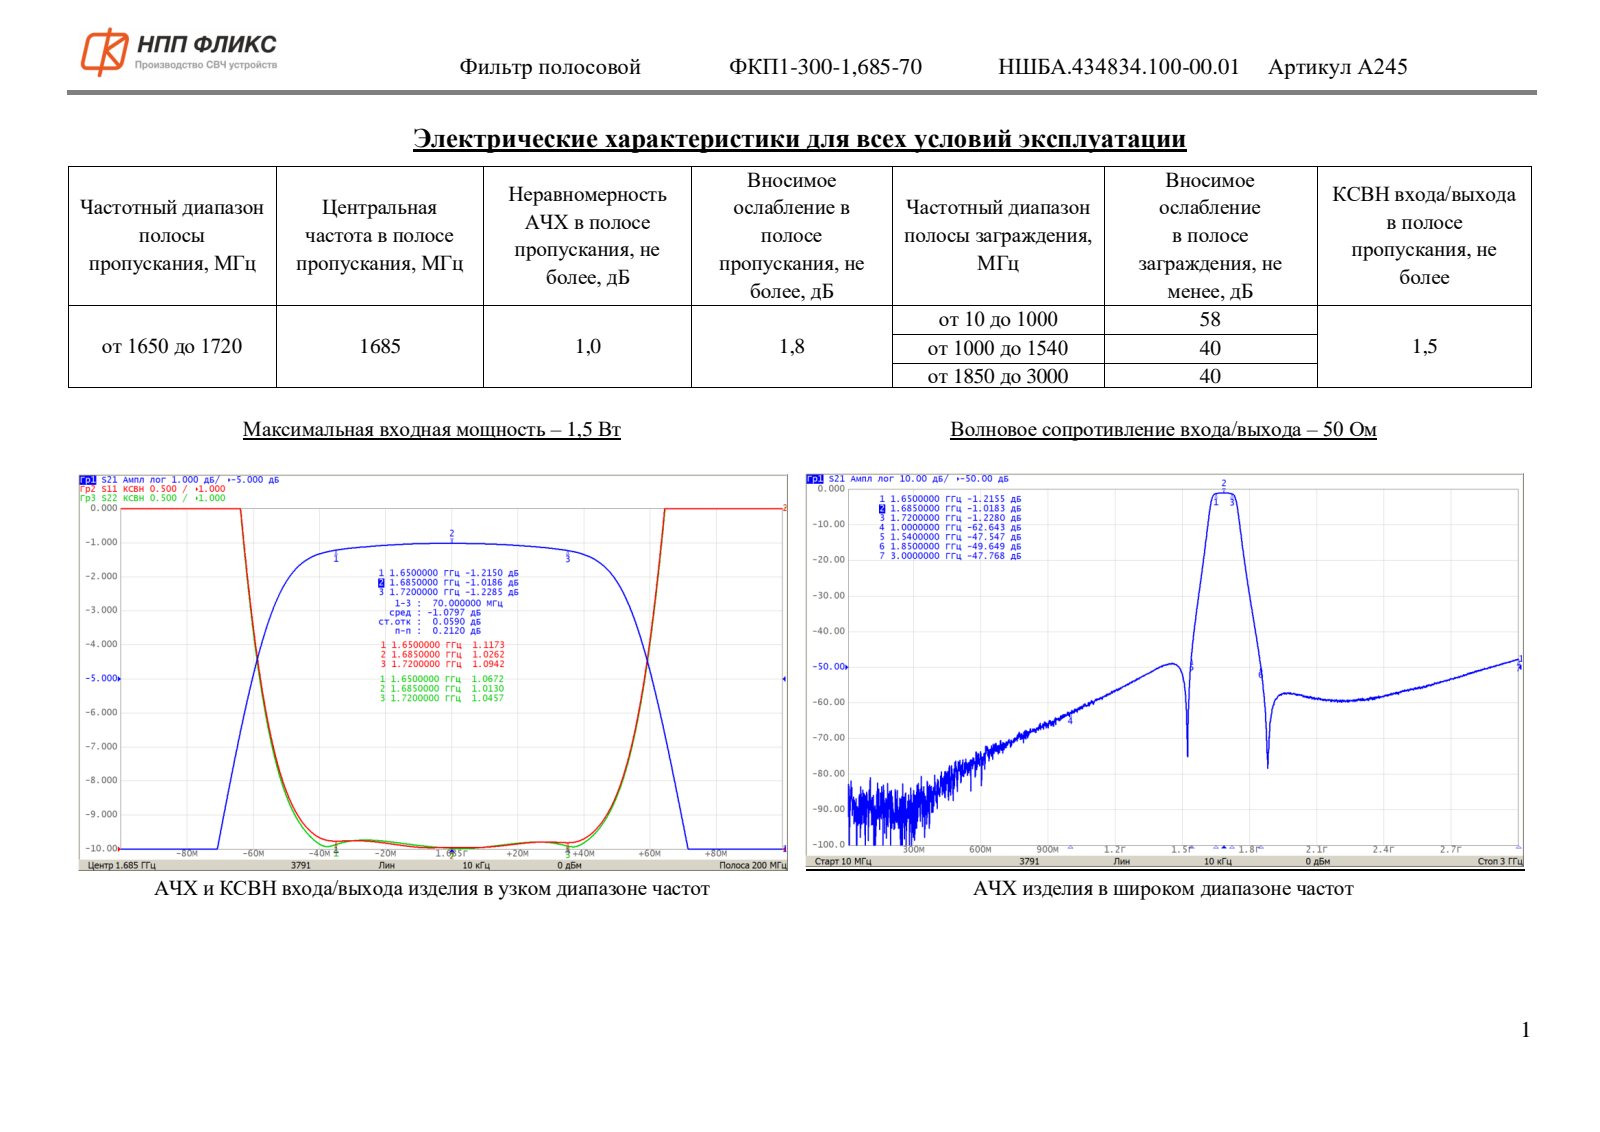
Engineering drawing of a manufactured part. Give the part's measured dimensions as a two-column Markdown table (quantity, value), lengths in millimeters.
| quantity | value |
| --- | --- |
| part name | НШБА.434834.100_Фильтр ФКП1-300-1,685-70 |
| STEP written by | ASCON Math Kernel (CONFIG_CONTROL_DESIGN) |
| units | millimeters |
| bodies | 2 solids, 461 faces (287 planar, 25 cylindrical, 149 other) |
| overall size | 10 × 7.3 × 3.9 |
| volume | 218 mm³ |
| surface area | 446 mm² |
| round holes (diameter × count) | 0.95 × 4 |
| partial cylindrical surfaces (radius × count) | 0.9 × 4, 0.12 × 3, 1.2 × 2, 0.18 × 1, 0.21 × 1, 0.3 × 1, 0.6 × 1 |
| main face-to-face distances | 3.6, 6, 3.9, 7, 1.3, 1, 7.3, 10, 9.75, 4.32 |
| hole center spacings | 2.26, 4.5, 2.24, 6.76 |
